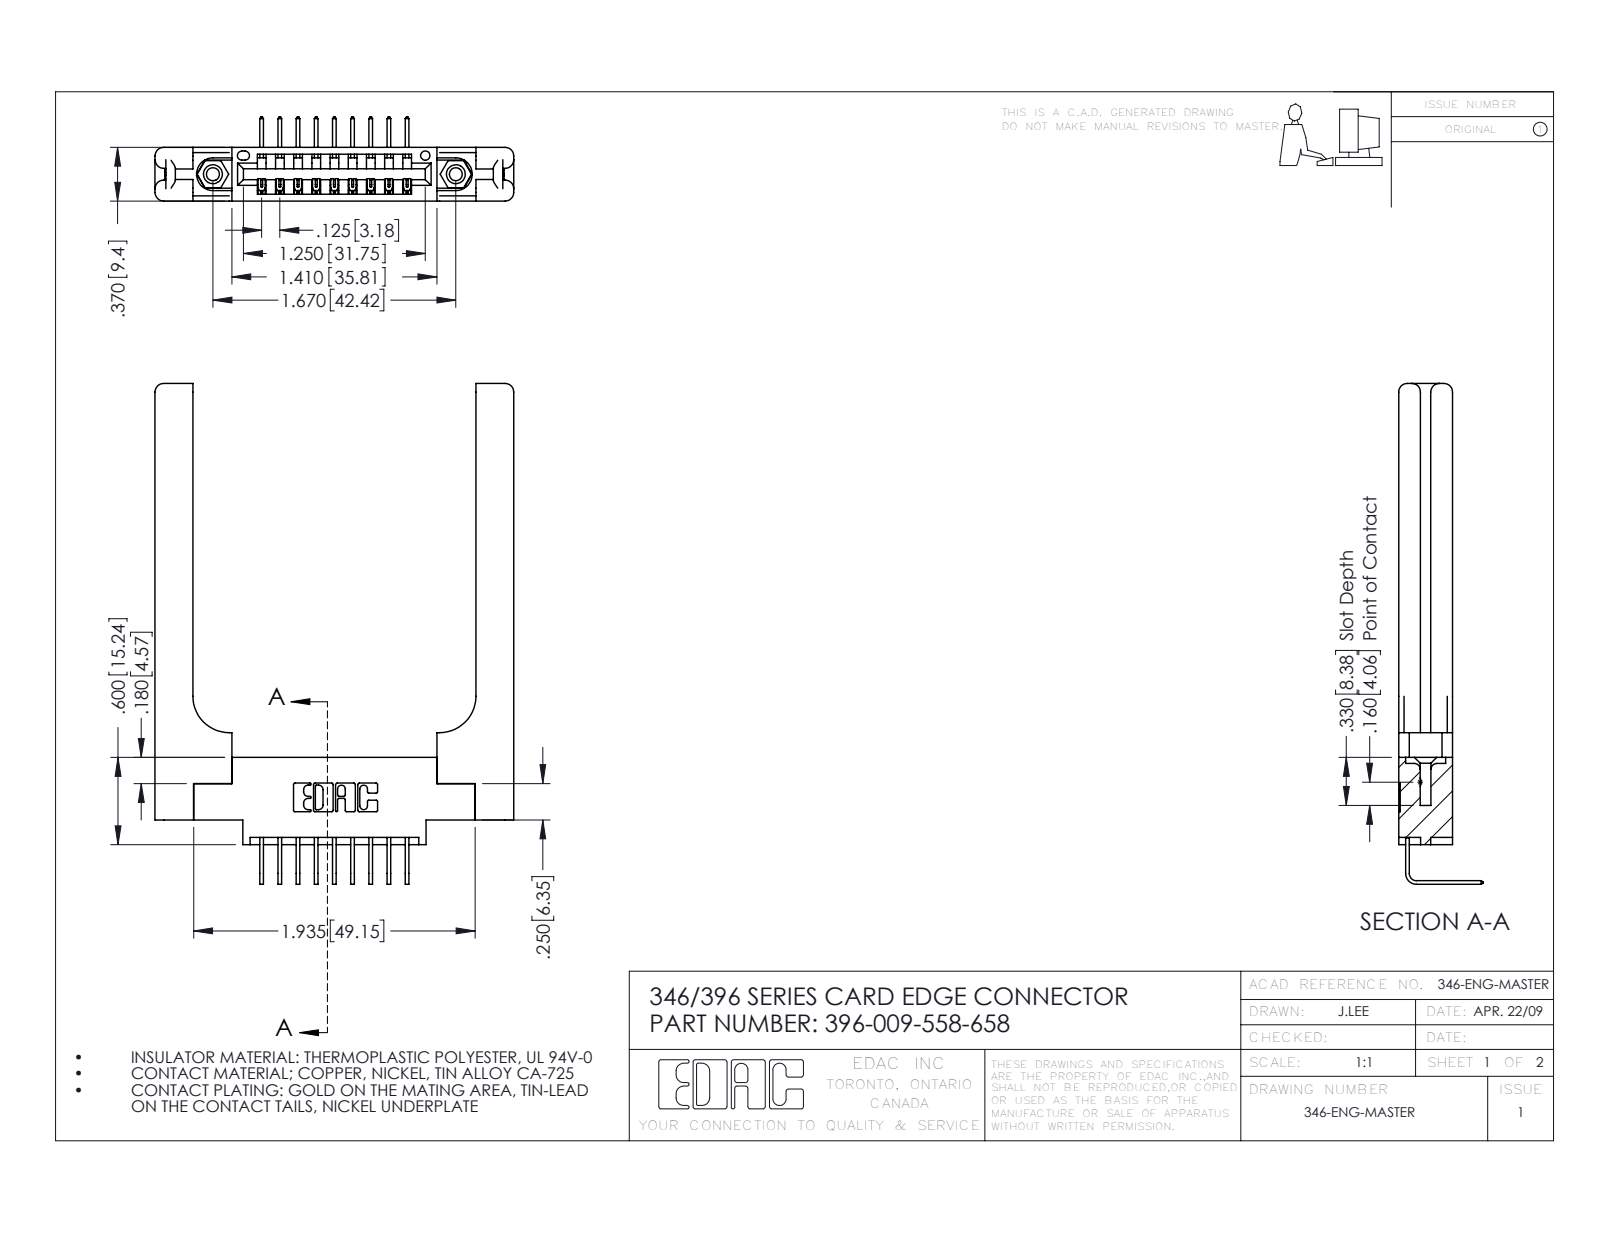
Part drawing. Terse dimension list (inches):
name: 346-220-058_345-220-058; 346 Part_0.170 Offset - 0.156 Dia-TH; 345-250-001_345-250-001-102; 345-292-001_558 Tail - 2 (+1 more)
written by: SolidWorks 2016 (CONFIG_CONTROL_DESIGN)
unit: in
bodies: 14 solids, 922 faces (606 planar, 256 cylindrical, 60 other)
size: 3.443 × 2.466 × 0.58
volume: 0.803 in³; area: 18.92 in²
holes: 2× ⌀0.089, 2× ⌀0.125, 2× ⌀0.156, 1× ⌀0.064
bosses: 2× ⌀0.155
rounds: 22× R0.01, 18× R0.006, 16× R0.06, 6× R0.007, 6× R0.031, 3× R0.026, 2× R0.03, 2× R0.031
face distances: 0.37, 0.15, 0.22, 0.072, 0.148, 0.322, 0.25, 0.048, 0.102, 0.173
hole spacings: 0.246, 1.465, 1.67
